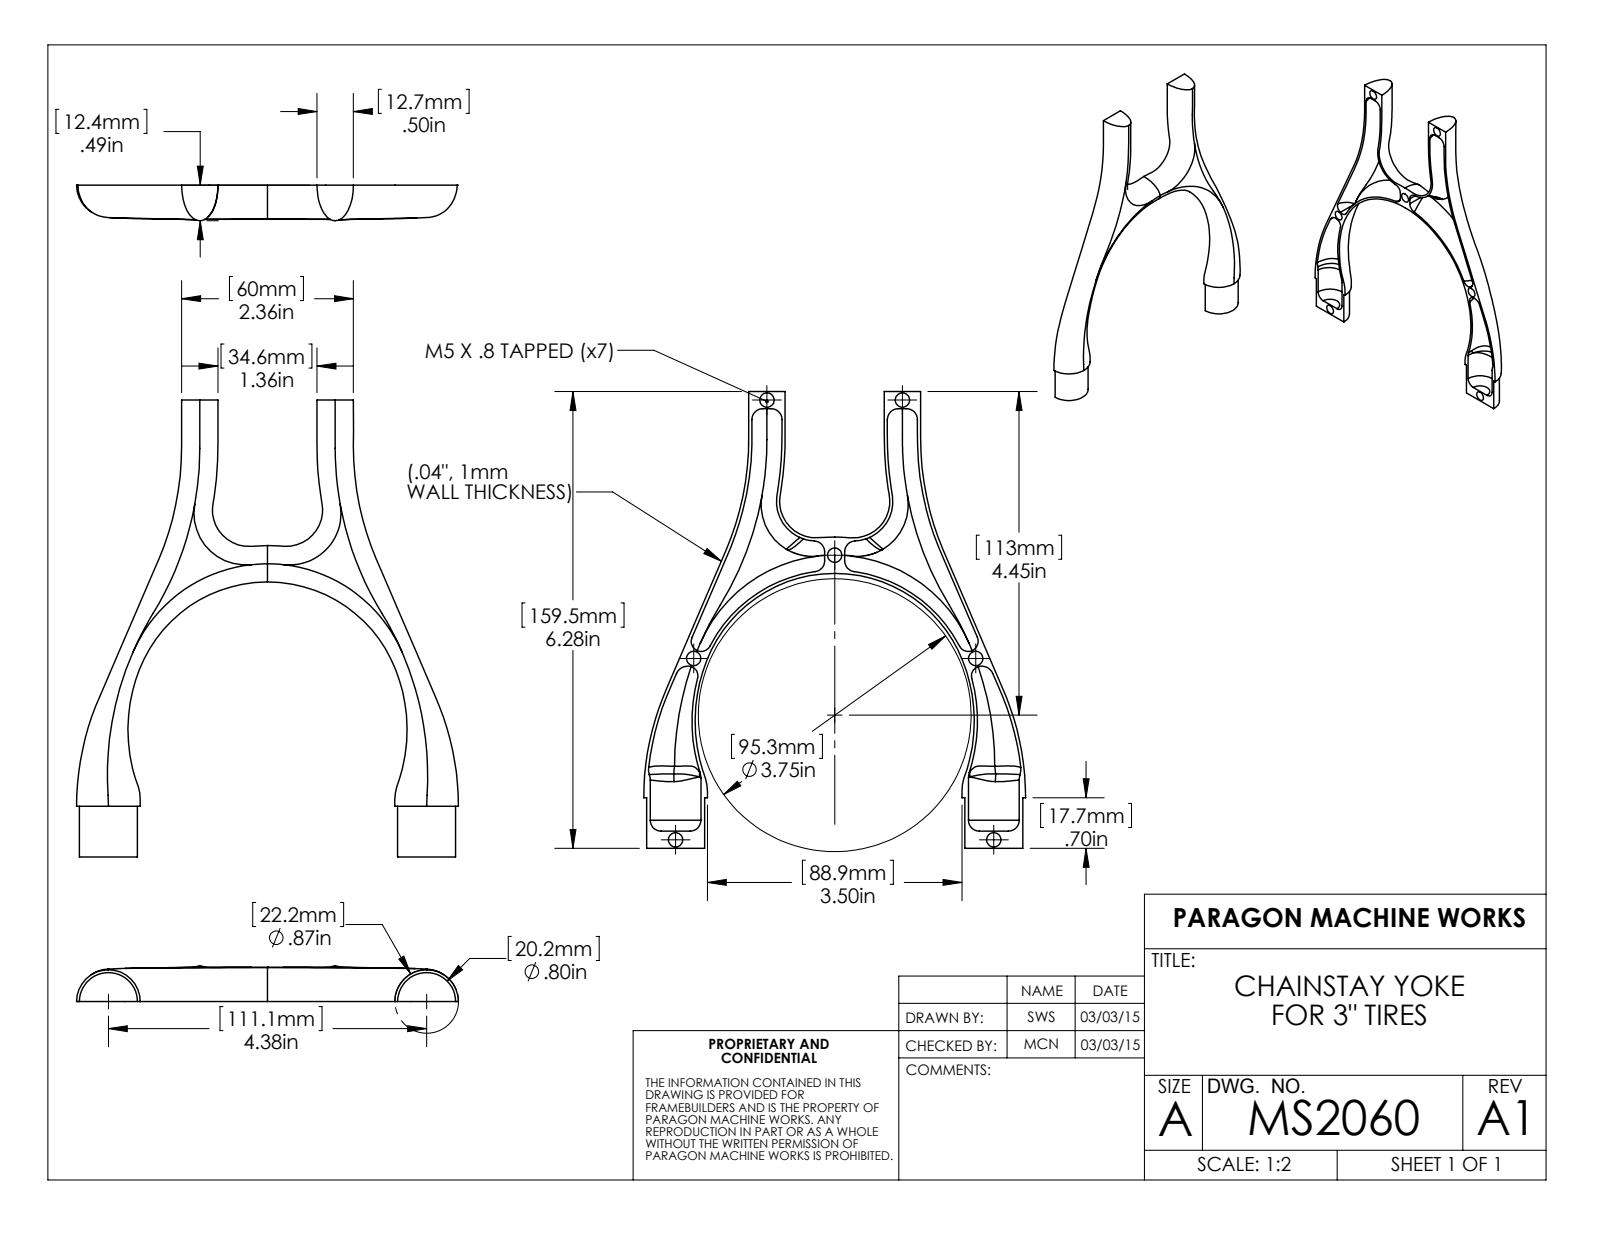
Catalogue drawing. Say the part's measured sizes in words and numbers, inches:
The part is named "MS2060". Its 3-D file was written by "SolidWorks 2012 (AUTOMOTIVE_DESIGN)". It is 1 solid with 83 faces: 24 planar, 27 cylindrical and 32 other. Overall it measures 6.29 by 5.25 by 1.202 inches. Its volume is 0.934 cubic inches and its surface area 36.69 square inches. Round holes: 7 of diameter 0.197. Partial cylindrical surfaces (rounded edges, fillets, slot ends): 6 of radius 0.15, 2 of radius 0.13, 2 of radius 0.134, 2 of radius 0.139, 2 of radius 0.149, 2 of radius 0.167, 2 of radius 0.348, 2 of radius 0.398. The main face-to-face distances are 0.043, 6.281, 0.237, 6.044, 0.697, 0.46, 5.583, 6.045, 5.808, 5.348. The hole center spacings are 2.326, 2.403, 2.505, 3.691, 4.482, 4.565, 4.821, 6.172.
